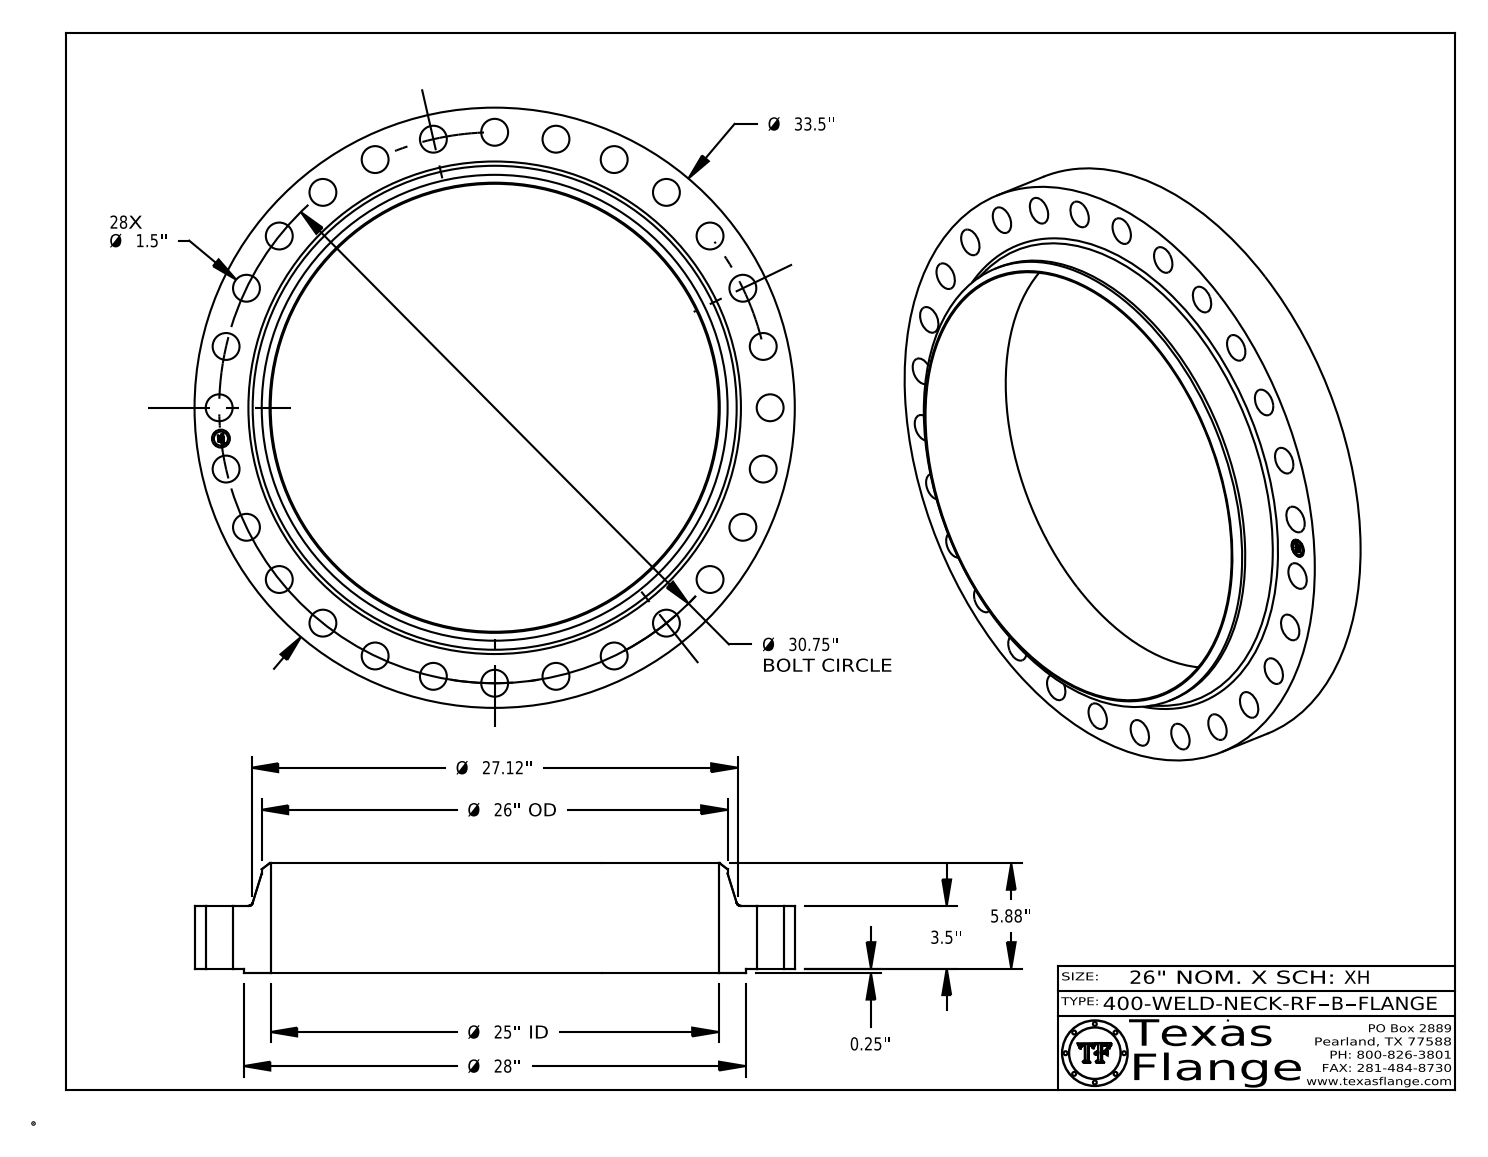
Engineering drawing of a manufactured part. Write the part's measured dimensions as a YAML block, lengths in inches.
part_name: "400-WELD-NECK-RF, Series B"
step_written_by: "CATIA V5 STEP AP214 (AUTOMOTIVE_DESIGN)"
units: inches
bodies: {solids: 1, faces: 459, planar: 369, cylindrical: 84, other: 6}
overall_size: [33.5, 33.5, 6.13]
volume: 1357
surface_area: 2151
round_holes:
  - {diameter: 1.5, count: 28}
  - {diameter: 1, count: 1}
  - {diameter: 25, count: 1}
round_bosses_or_shafts:
  - {diameter: 0.061, count: 8}
  - {diameter: 33.5, count: 1}
  - {diameter: 28, count: 1}
  - {diameter: 26, count: 1}
  - {diameter: 0.788, count: 1}
face_to_face_distances: [3.5, 0.25, 3.75, 6.13, 5.88, 2.38, 3.735, 3.485, 0.015, 2.395]
hole_center_spacings: [6.843, 29.024, 15.375, 21.743, 13.342, 16.36, 19.172, 26.037]
